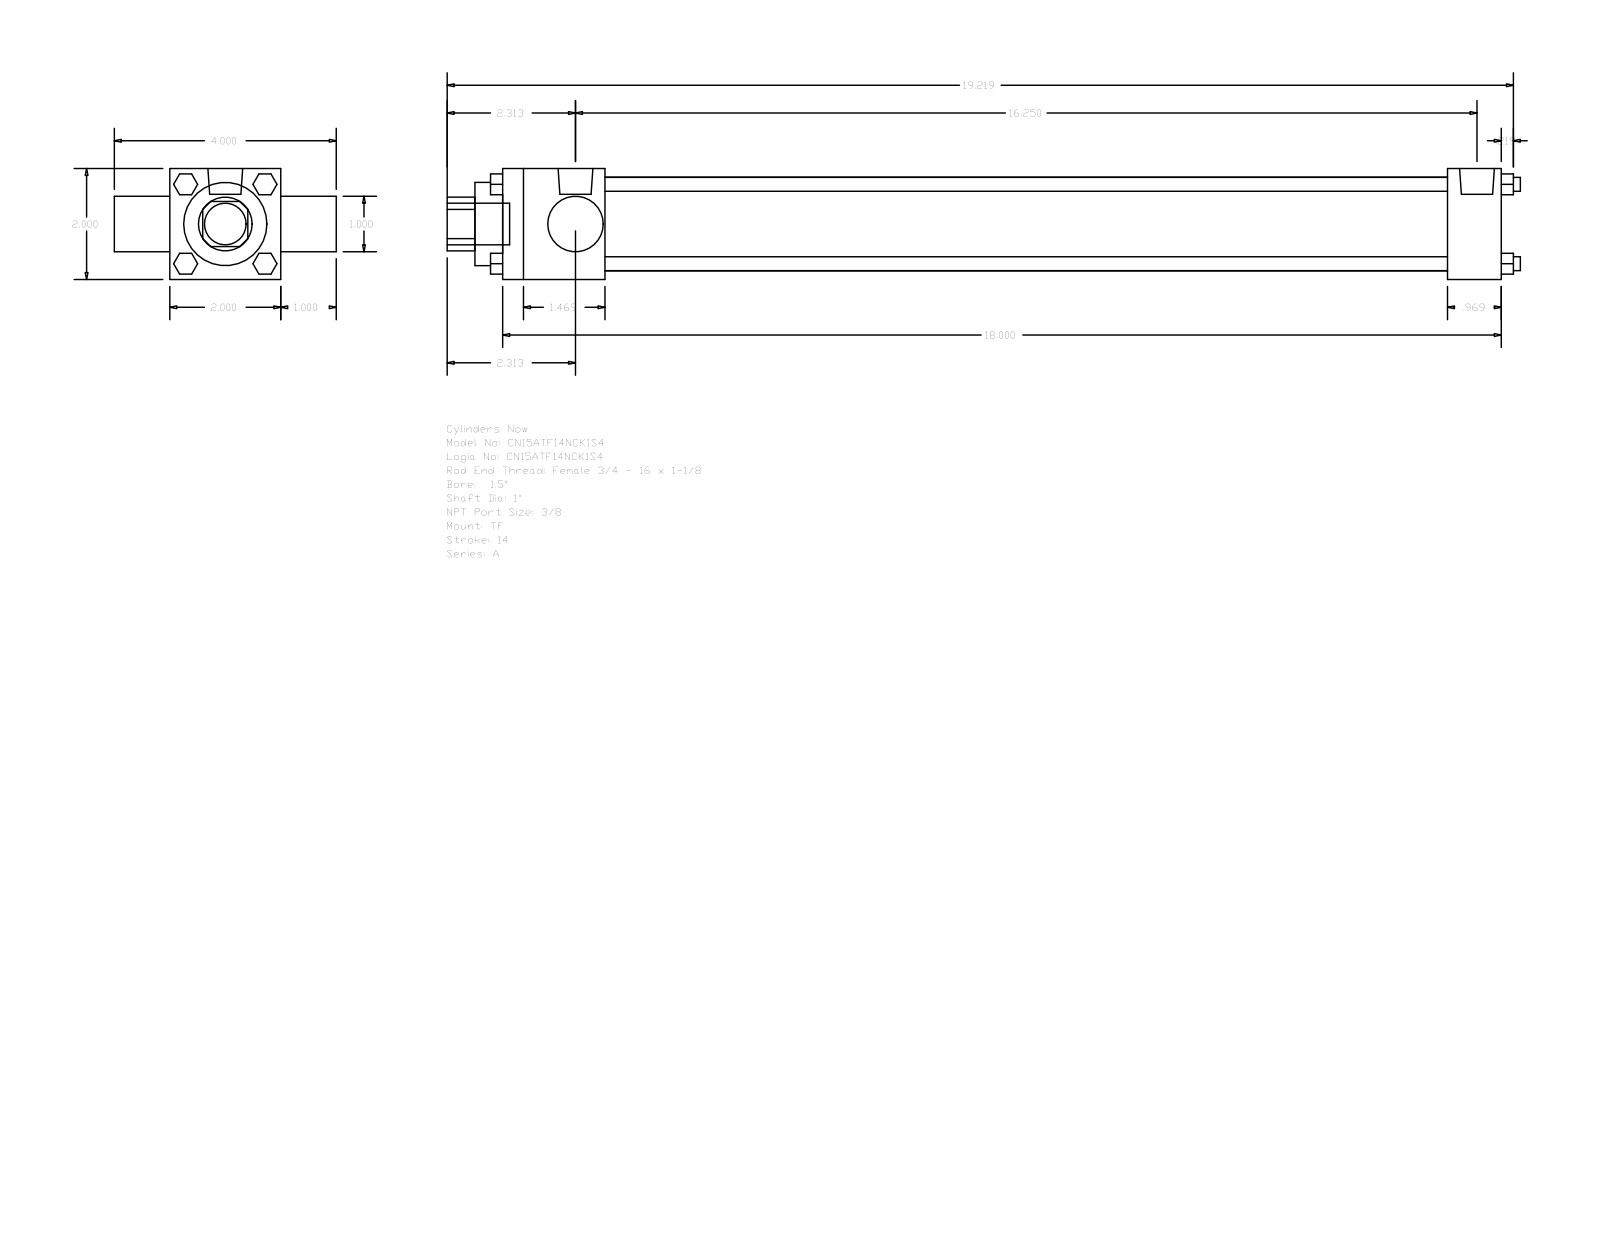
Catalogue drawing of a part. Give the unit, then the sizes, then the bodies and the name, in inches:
Units: inches
Overall size (bounding box): 19.344 × 4 × 2
Round holes (diameter × count): ⌀1 ×2, ⌀1.5 ×1, ⌀1.69 ×1
Round bosses / shafts (diameter × count): ⌀0.25 ×4, ⌀0.219 ×3, ⌀0.627 ×2, ⌀0.75 ×1
Partial cylindrical surfaces — rounded edges, fillets, slot ends (radius × count): R0.484 ×1
Main face-to-face distances: 2, 1, 18, 3, 1.844, 17.031, 15.187, 16.156, 0.969, 0.5
Bodies: 0 solids, 120 faces (92 planar, 28 cylindrical, 0 other)
Part name (STEP PRODUCT): A_TF__0150_1
STEP written by: GSSL Pune (CONFIG_CONTROL_DESIGN)
